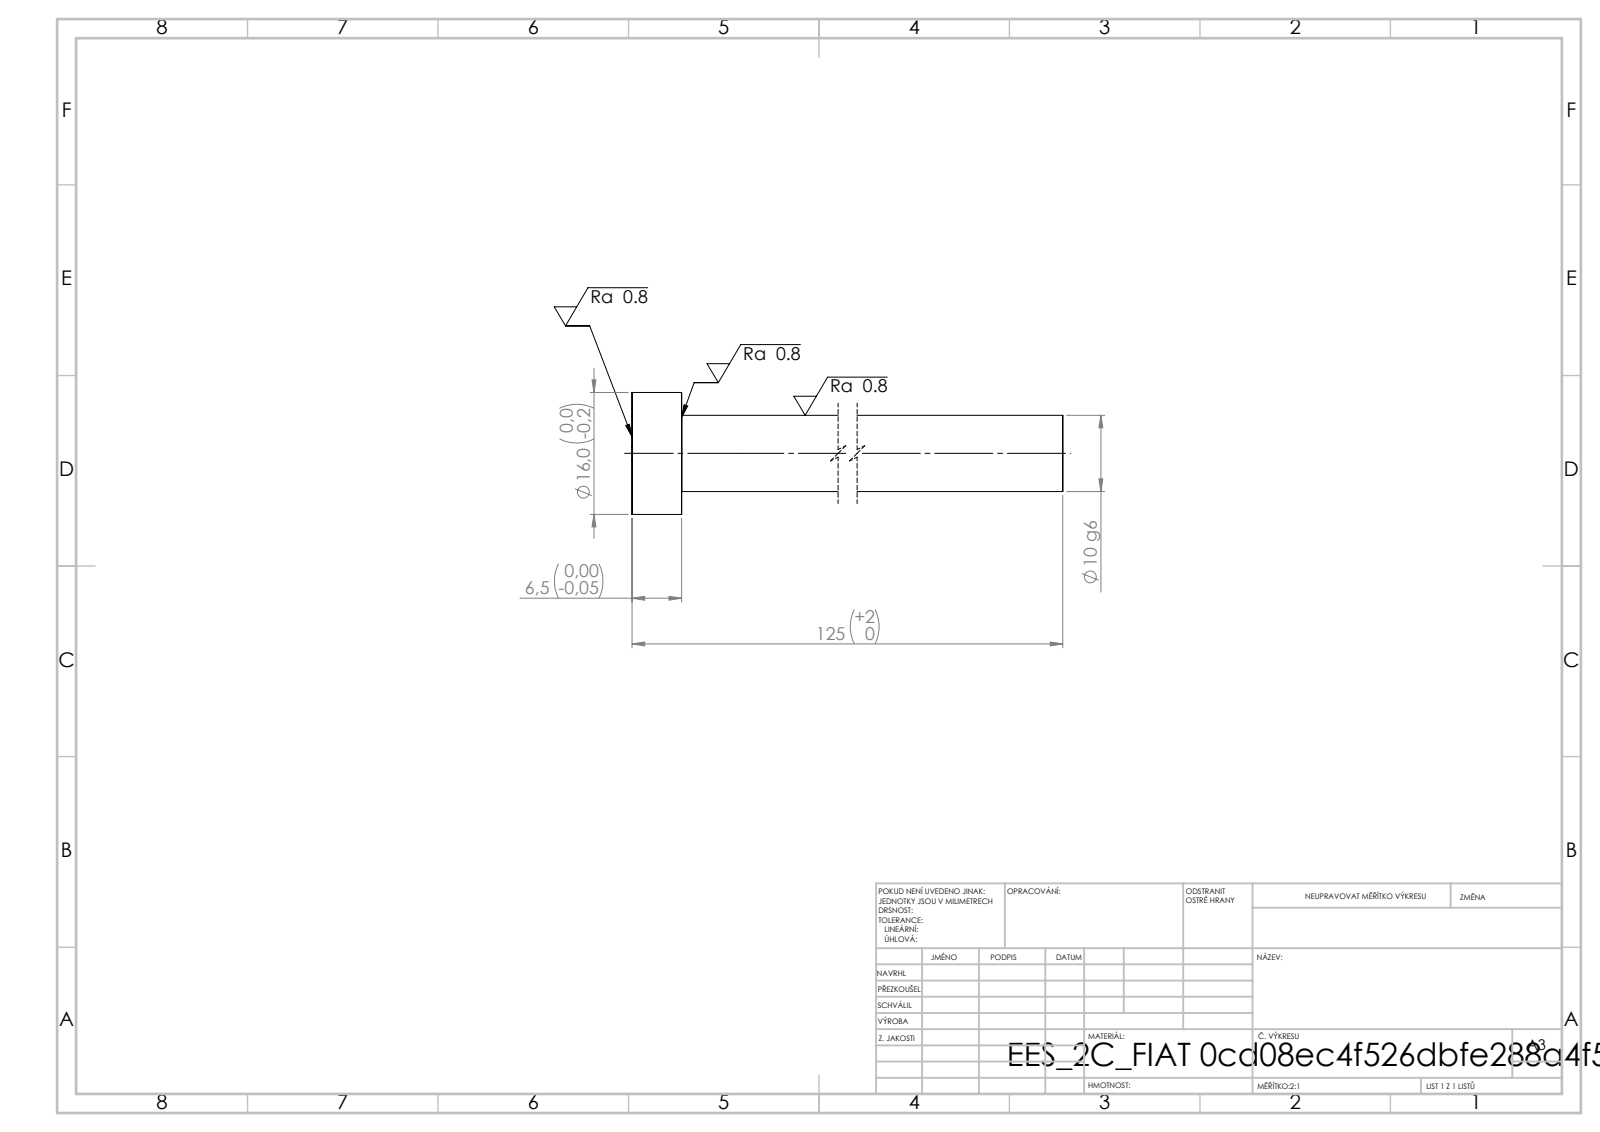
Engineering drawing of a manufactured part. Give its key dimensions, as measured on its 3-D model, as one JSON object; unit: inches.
{"step_written_by": "SolidWorks 2019 (CONFIG_CONTROL_DESIGN)", "units": "inches", "bodies": {"solids": 1, "faces": 7, "planar": 3, "cylindrical": 4, "other": 0}, "overall_size": [4.921, 0.63, 0.63], "volume_in3": 0.648, "surface_area_in2": 6.901, "round_bosses_or_shafts": [[0.63, 1], [0.394, 1]], "face_to_face_distances": [0.256, 4.921, 4.665]}
